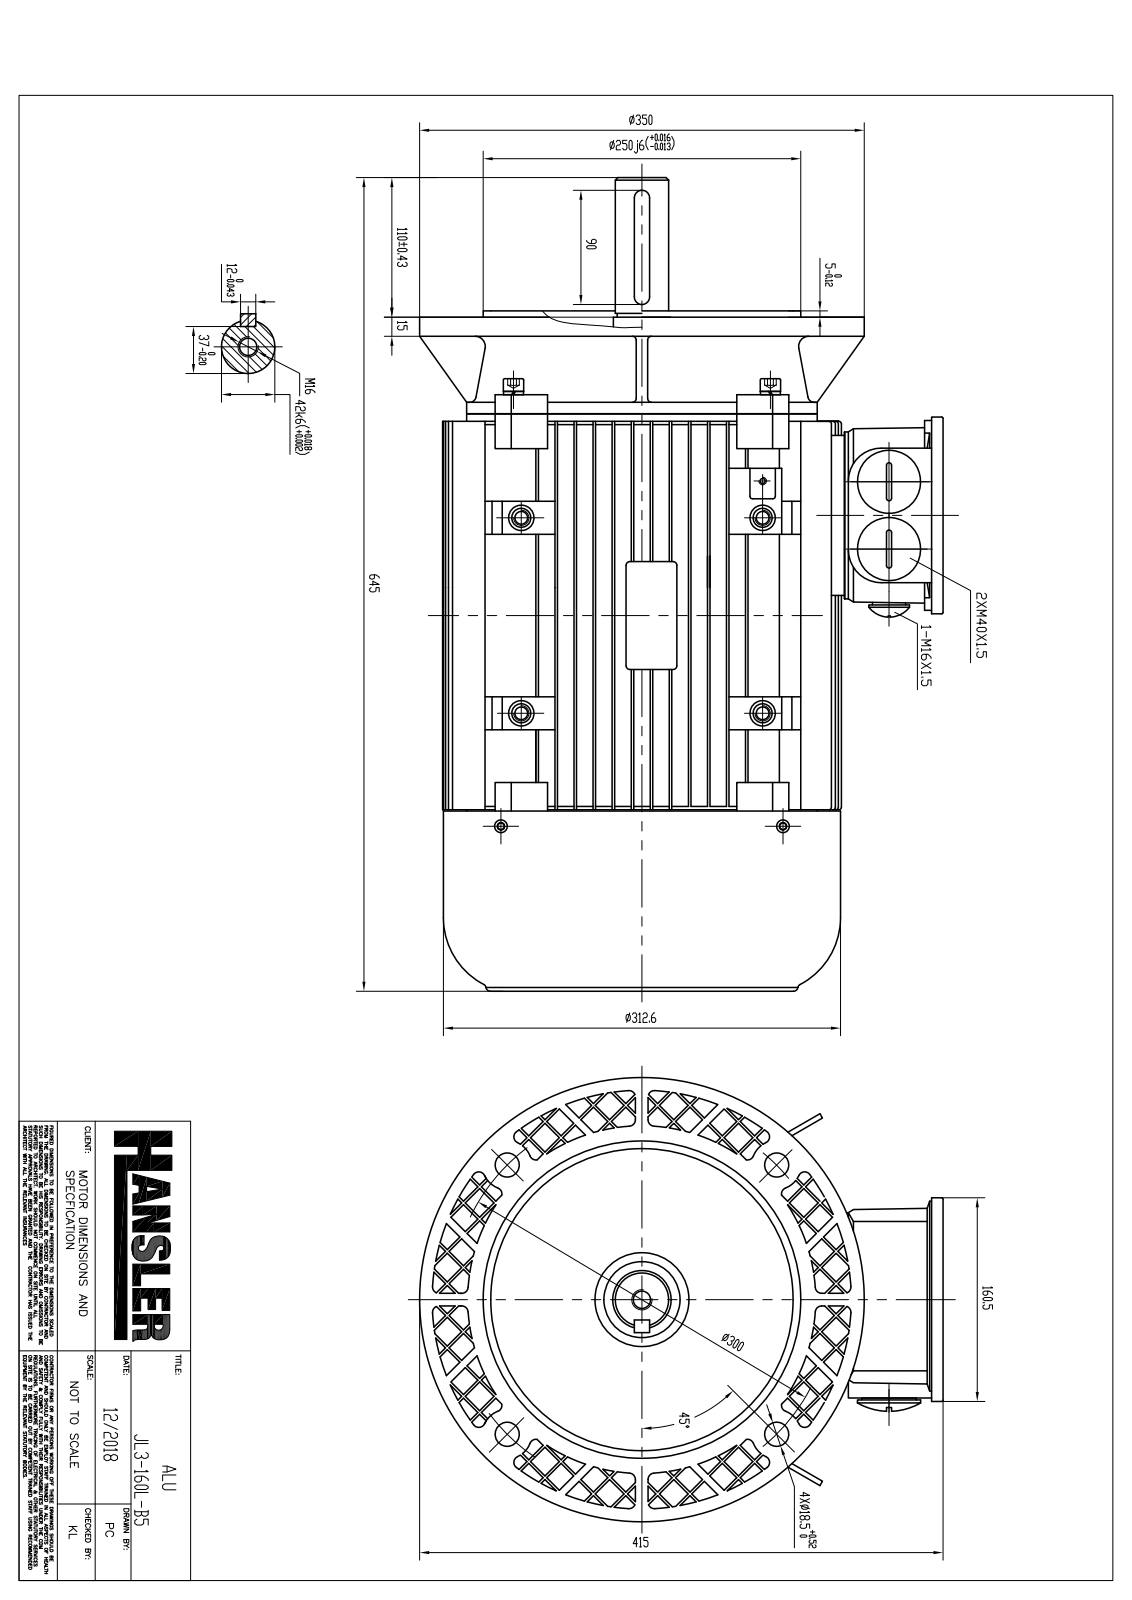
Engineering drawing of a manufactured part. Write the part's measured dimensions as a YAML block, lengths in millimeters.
part_name: "jl09144554h2ac"
step_written_by: "SIEMENS PLM Software NX 8.0 (AUTOMOTIVE_DESIGN)"
units: millimeters
bodies: {solids: 56, faces: 7676, planar: 3681, cylindrical: 1851, other: 2144}
overall_size: [633, 417.7, 350]
volume: 7259000
surface_area: 2710000
round_holes:
  - {diameter: 5, count: 28}
  - {diameter: 4.12, count: 12}
  - {diameter: 8.39, count: 8}
  - {diameter: 9.1, count: 8}
  - {diameter: 10, count: 8}
  - {diameter: 12, count: 8}
  - {diameter: 21, count: 8}
  - {diameter: 5.25, count: 5}
  - {diameter: 5.3, count: 5}
  - {diameter: 8, count: 5}
  - {diameter: 4.2, count: 4}
  - {diameter: 5.48, count: 4}
round_bosses_or_shafts:
  - {diameter: 8, count: 10}
  - {diameter: 5.38, count: 9}
  - {diameter: 15, count: 8}
  - {diameter: 12.59, count: 8}
  - {diameter: 7.19, count: 8}
  - {diameter: 10, count: 5}
  - {diameter: 7.85, count: 5}
  - {diameter: 5, count: 5}
partial_cylinders:
  - {radius: 1.2, count: 262}
  - {radius: 1, count: 161}
  - {radius: 2, count: 68}
  - {radius: 1.37, count: 37}
  - {radius: 3.42, count: 25}
  - {radius: 3, count: 20}
  - {radius: 4, count: 20}
  - {radius: 0.81, count: 18}
face_to_face_distances: [15, 30, 45, 2, 60, 75, 13, 17, 90, 28]
hole_center_spacings: [202.36, 207.25, 14.64, 202.24, 207.24, 95.35, 134, 202.23]
